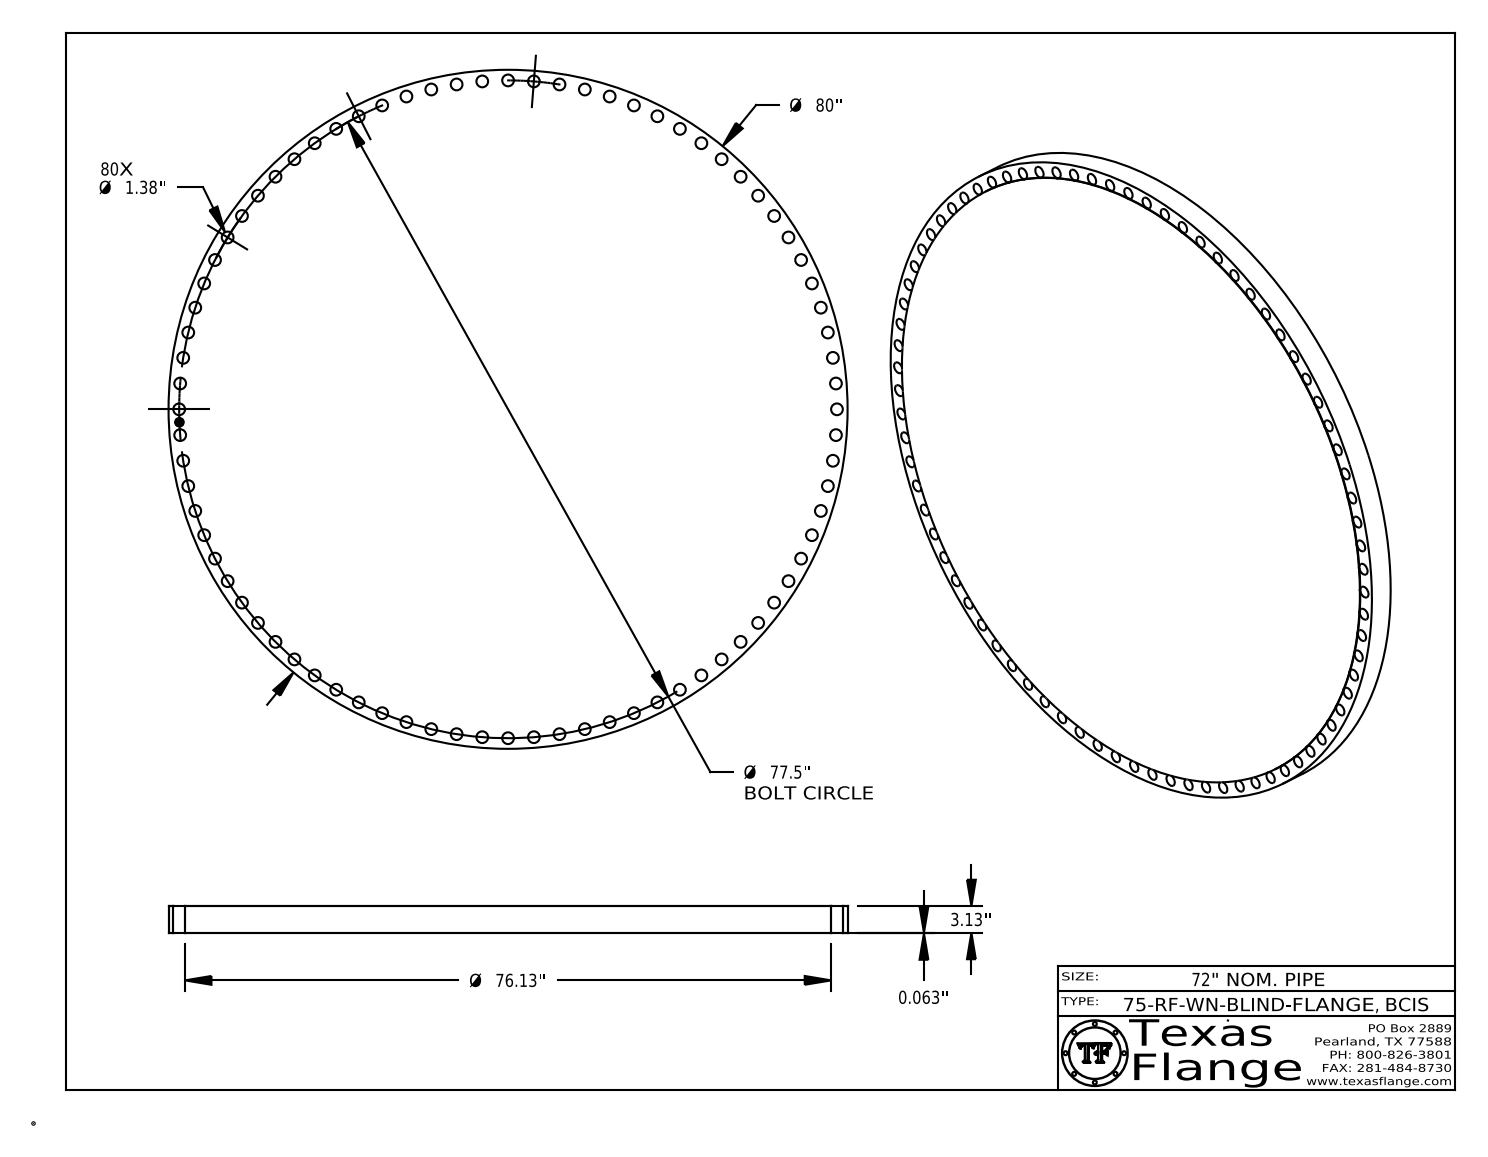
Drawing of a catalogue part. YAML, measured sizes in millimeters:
part_name: "75-RF-WN-BLIND, Series BCIS"
step_written_by: "CATIA V5 STEP AP214 (AUTOMOTIVE_DESIGN)"
units: millimeters
bodies: {solids: 1, faces: 632, planar: 368, cylindrical: 264, other: 0}
overall_size: [2032, 2032, 81.1]
volume: 256300000
surface_area: 7549000
round_holes:
  - {diameter: 35.1, count: 80}
  - {diameter: 25.4, count: 1}
round_bosses_or_shafts:
  - {diameter: 1.5, count: 8}
  - {diameter: 2032, count: 1}
  - {diameter: 1933.7, count: 1}
  - {diameter: 20, count: 1}
face_to_face_distances: [81.1, 1.6, 79.5, 0.4, 80.7, 79.1, 7.6, 7.4, 1.4, 4.9]
hole_center_spacings: [154.5, 307.9, 77.3, 231.4, 534.3, 459.5, 608.3, 1962.4]
